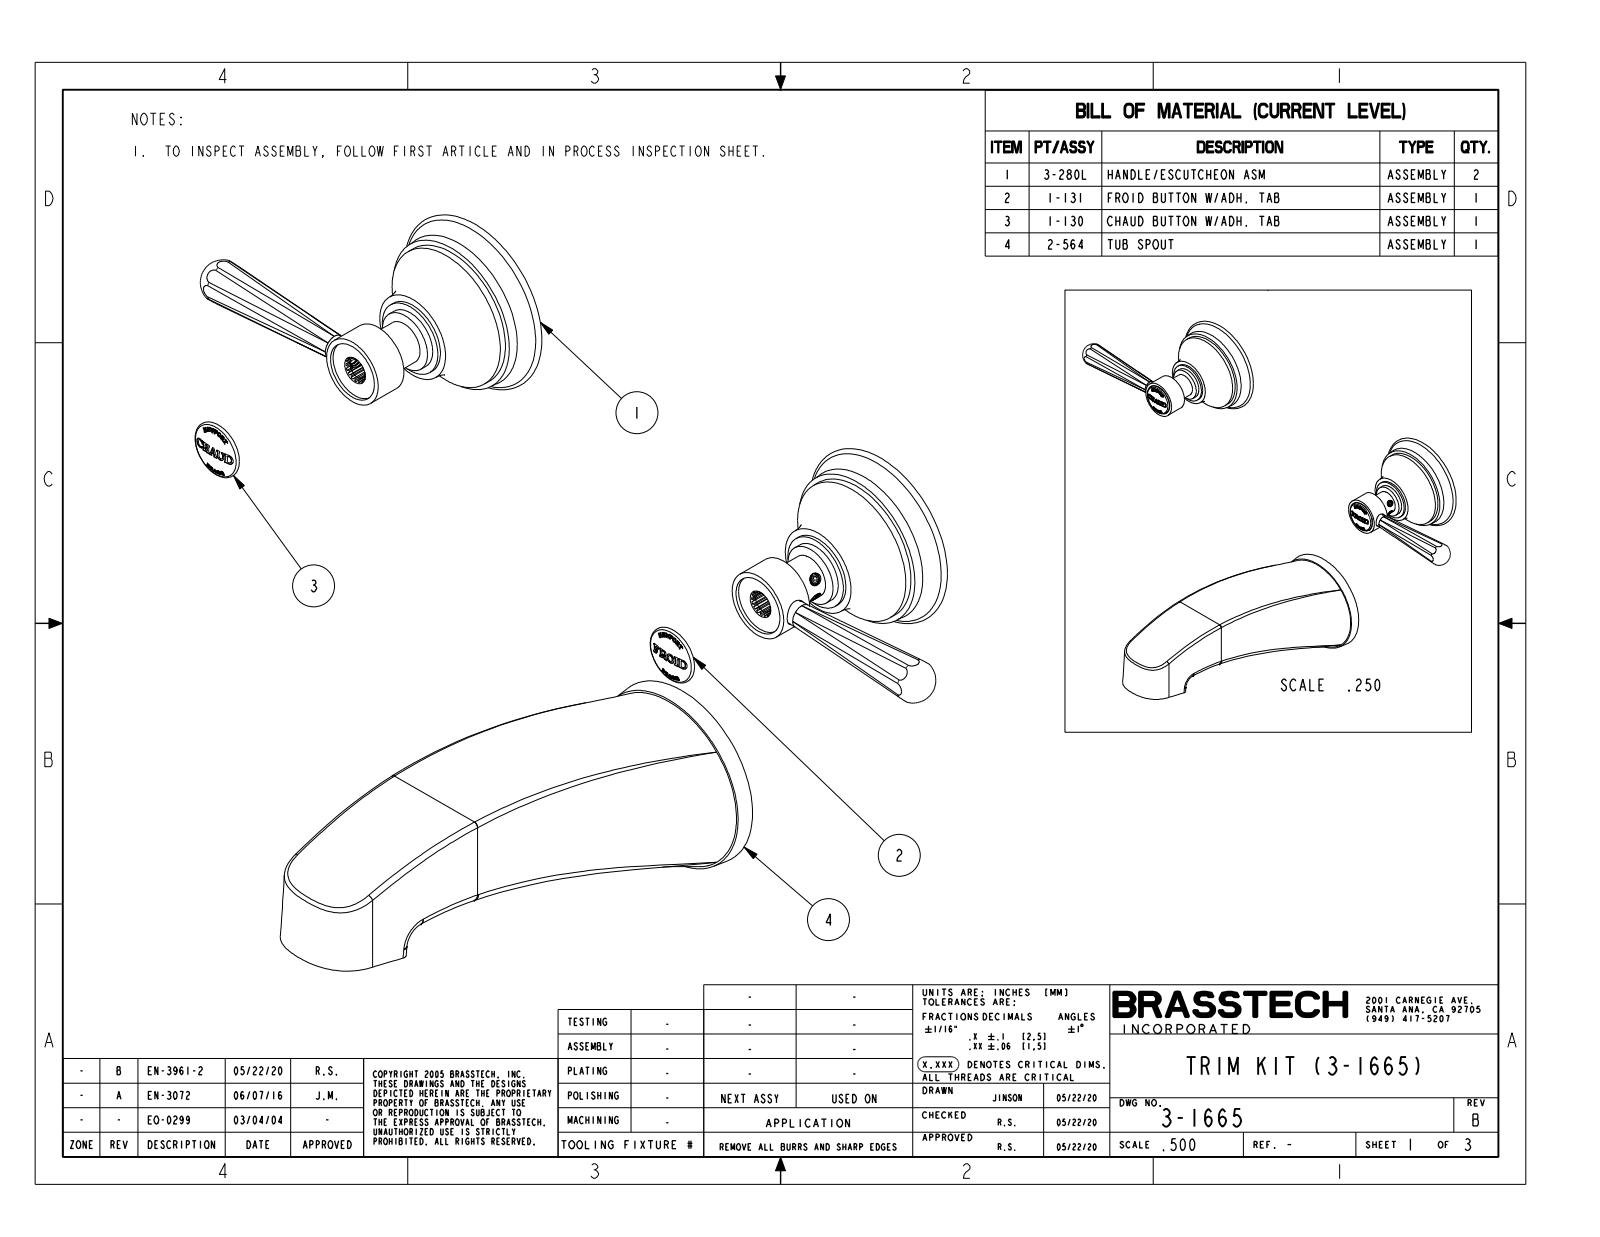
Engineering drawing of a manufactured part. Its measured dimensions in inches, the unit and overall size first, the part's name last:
Units: inches
Overall size (bounding box): 14.023 × 8.688 × 7.429
Round holes (diameter × count): ⌀0.85 ×2, ⌀0.363 ×1
Round bosses / shafts (diameter × count): ⌀2.1 ×2, ⌀1.075 ×2, ⌀1 ×2, ⌀0.875 ×2, ⌀0.625 ×2, ⌀0.5 ×2, ⌀0.35 ×1
Partial cylindrical surfaces — rounded edges, fillets, slot ends (radius × count): R0.011 ×28, R0.025 ×17, R0.006 ×14, R0.015 ×14, R0.005 ×10, R0.014 ×9, R0.006 ×8, R0.013 ×8
Main face-to-face distances: 0.062, 0.168, 2.407, 2.345, 0.537, 0.475, 1.87, 0.015, 2.422, 2.36
Hole centre spacings: 7.874
Volume: 32.45 in³ · Surface area: 106.4 in²
Bodies: 5 solids, 857 faces (414 planar, 280 cylindrical, 163 other)
Part name (STEP PRODUCT): 3-1665_SW0001
STEP written by: CREO PARAMETRIC BY PTC INC, 2018400 (AUTOMOTIVE_DESIGN)
